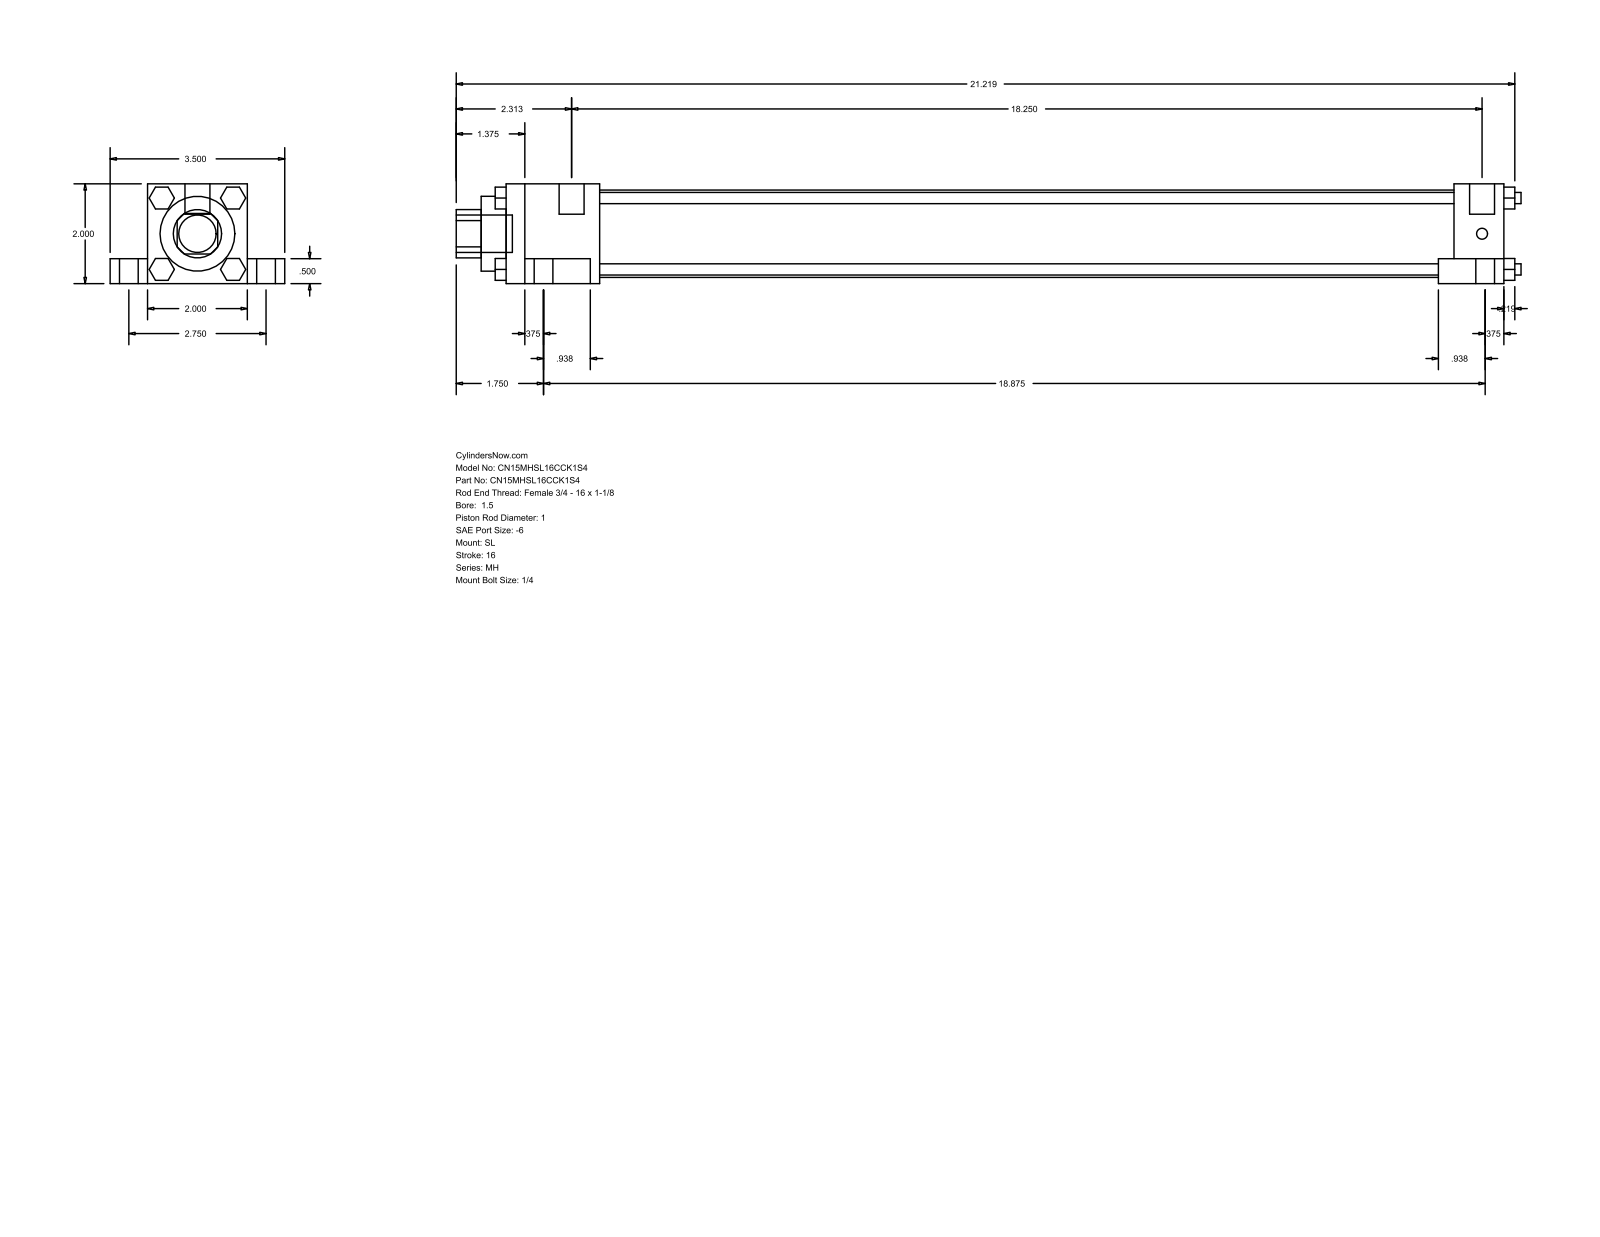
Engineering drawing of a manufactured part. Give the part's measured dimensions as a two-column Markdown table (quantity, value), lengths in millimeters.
| quantity | value |
| --- | --- |
| part name | MH_SL__0150_1 |
| STEP written by | GSSL Pune (CONFIG_CONTROL_DESIGN) |
| units | millimeters |
| bodies | 0 solids, 148 faces (112 planar, 36 cylindrical, 0 other) |
| overall size | 542.13 × 88.9 × 50.8 |
| round holes (diameter × count) | 25.4 × 1, 38.1 × 1, 44.45 × 1 |
| round bosses / shafts (diameter × count) | 15.88 × 4, 9.53 × 4, 5.71 × 4, 5.56 × 4, 12.7 × 2, 19.05 × 1 |
| partial cylindrical surfaces (radius × count) | 12.29 × 1 |
| main face-to-face distances | 50.8, 12.7, 38.1, 19.05, 69.85, 508, 25.4, 9.52, 33.34, 465.14 |
